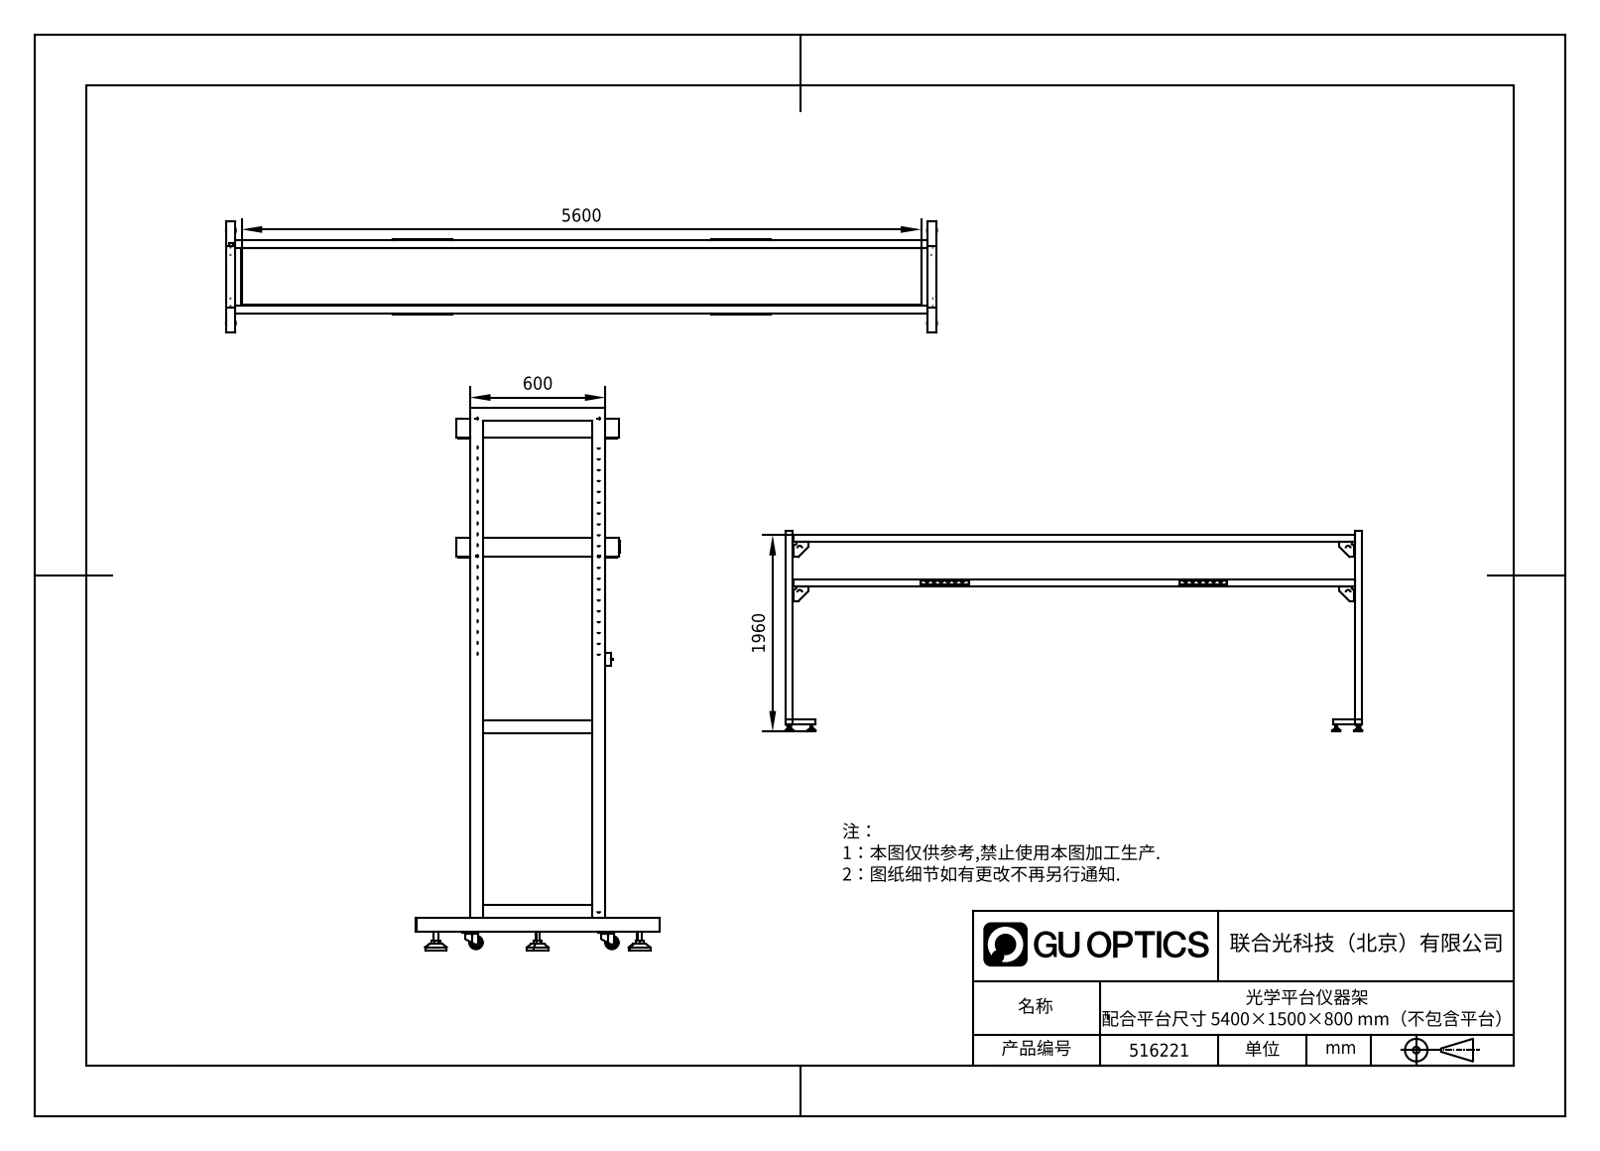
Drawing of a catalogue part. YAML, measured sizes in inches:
part_name: "516221"
step_written_by: "SolidWorks 2020 (AUTOMOTIVE_DESIGN)"
units: inches
bodies: {solids: 55, faces: 2591, planar: 1443, cylindrical: 1072, other: 76}
overall_size: [226.378, 78.78, 35.433]
volume: 2359
surface_area: 46470
round_holes:
  - {diameter: 0.354, count: 66}
  - {diameter: 0.24, count: 16}
  - {diameter: 0.394, count: 16}
  - {diameter: 0.256, count: 12}
  - {diameter: 0.165, count: 8}
  - {diameter: 0.205, count: 8}
  - {diameter: 0.236, count: 8}
  - {diameter: 0.669, count: 6}
  - {diameter: 0.709, count: 6}
  - {diameter: 1.024, count: 6}
  - {diameter: 2.717, count: 6}
  - {diameter: 0.126, count: 4}
round_bosses_or_shafts:
  - {diameter: 3.15, count: 6}
  - {diameter: 0.63, count: 6}
  - {diameter: 1.024, count: 4}
  - {diameter: 0.709, count: 4}
  - {diameter: 1.969, count: 2}
  - {diameter: 0.394, count: 2}
partial_cylinders:
  - {radius: 0.197, count: 36}
  - {radius: 0.276, count: 24}
  - {radius: 0.118, count: 16}
  - {radius: 0.167, count: 12}
  - {radius: 0.059, count: 8}
  - {radius: 0.059, count: 8}
  - {radius: 0.158, count: 8}
  - {radius: 0.512, count: 4}
face_to_face_distances: [17.323, 0.059, 0.118, 2.756, 17.264, 2.638, 0.098, 2.657, 17.382, 20.866]
hole_center_spacings: [1.575, 3.15, 4.724, 11.024, 6.299, 7.874, 9.449, 12.598]
